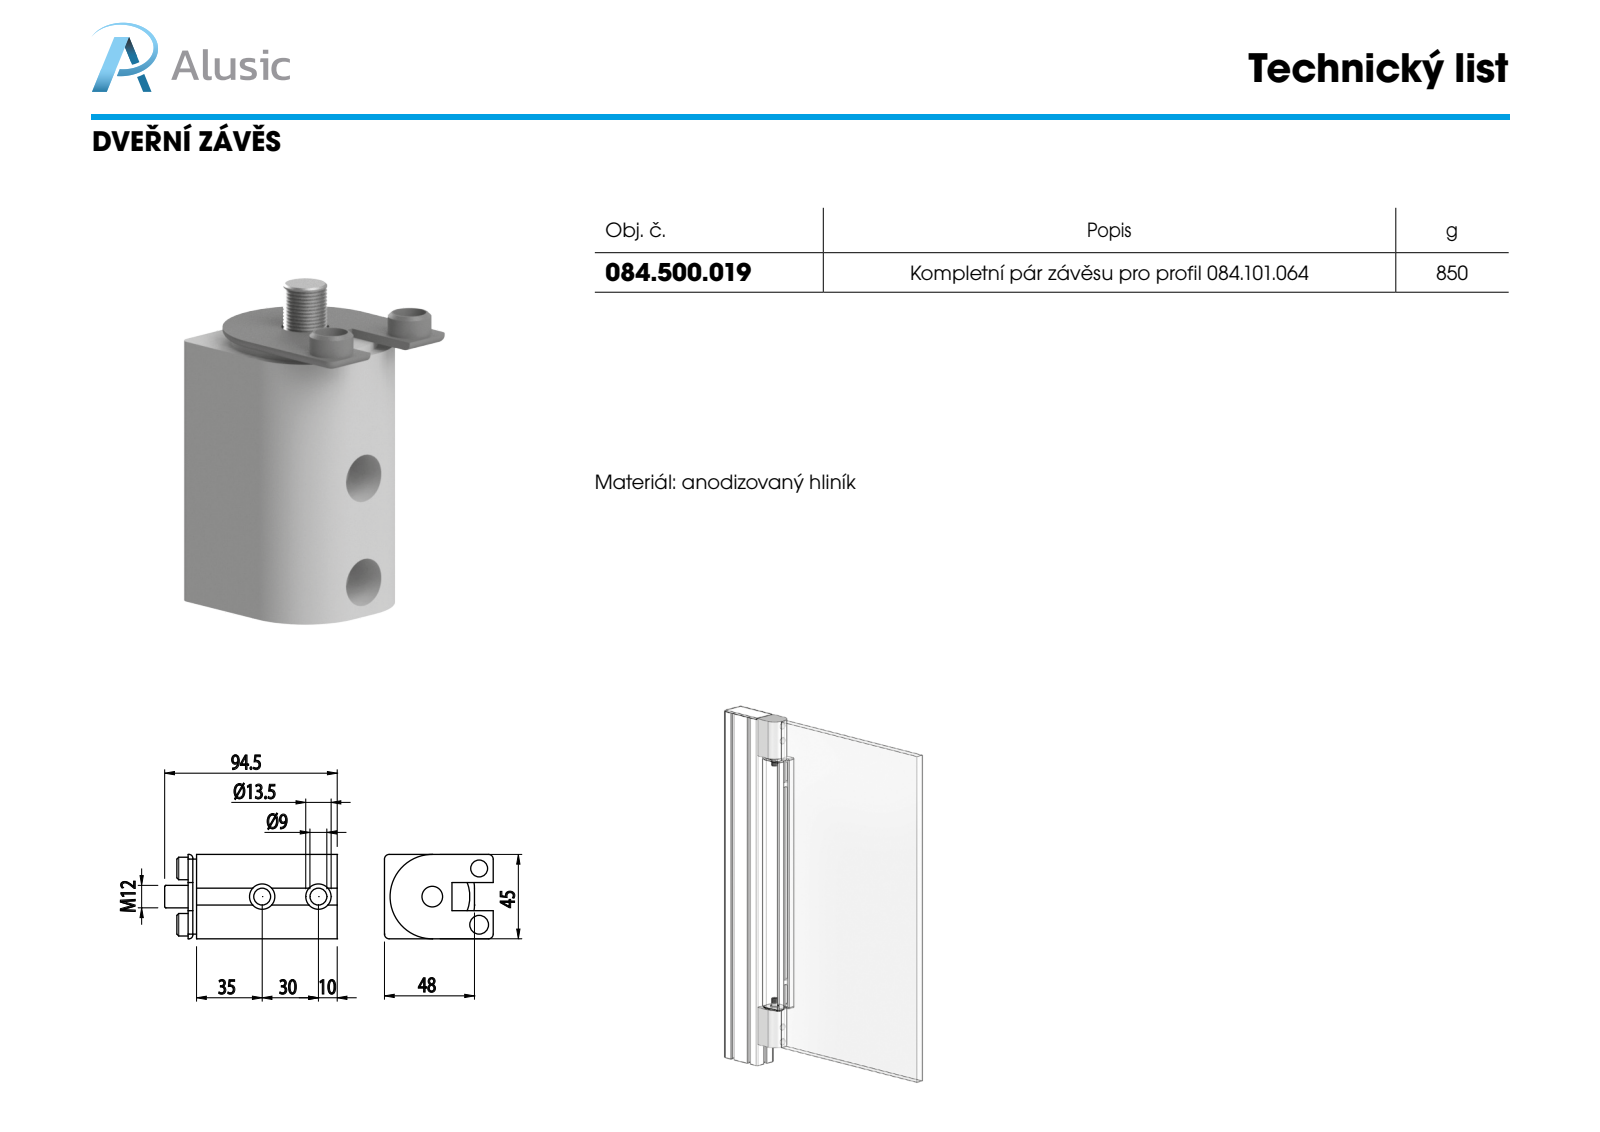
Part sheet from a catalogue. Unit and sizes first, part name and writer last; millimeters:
Units: millimetres
Overall size (bounding box): 92 × 58 × 45
Round holes (diameter × count): ⌀9 ×4, ⌀13.5 ×2, ⌀4 ×1, ⌀13 ×1, ⌀17 ×1, ⌀30 ×1, ⌀40 ×1
Round bosses / shafts (diameter × count): ⌀12 ×3, ⌀29.9 ×1
Partial cylindrical surfaces — rounded edges, fillets, slot ends (radius × count): R2.5 ×4, R2 ×3, R18 ×2, R22.5 ×1
Main face-to-face distances: 45, 77, 79.5, 2.5, 15, 5, 70, 7, 9.5, 22
Hole centre spacings: 29.15, 30, 30.45, 1.5
Volume: 148 975 mm³ · Surface area: 33 126 mm²
Bodies: 4 solids, 98 faces (31 planar, 48 cylindrical, 19 other)
Part name (STEP PRODUCT): 084.500.019; 084.500.019C_B; 084.500.019B; 084.201.073_Default<A macchina> (+1 more)
STEP written by: SolidWorks 2016 (CONFIG_CONTROL_DESIGN)
